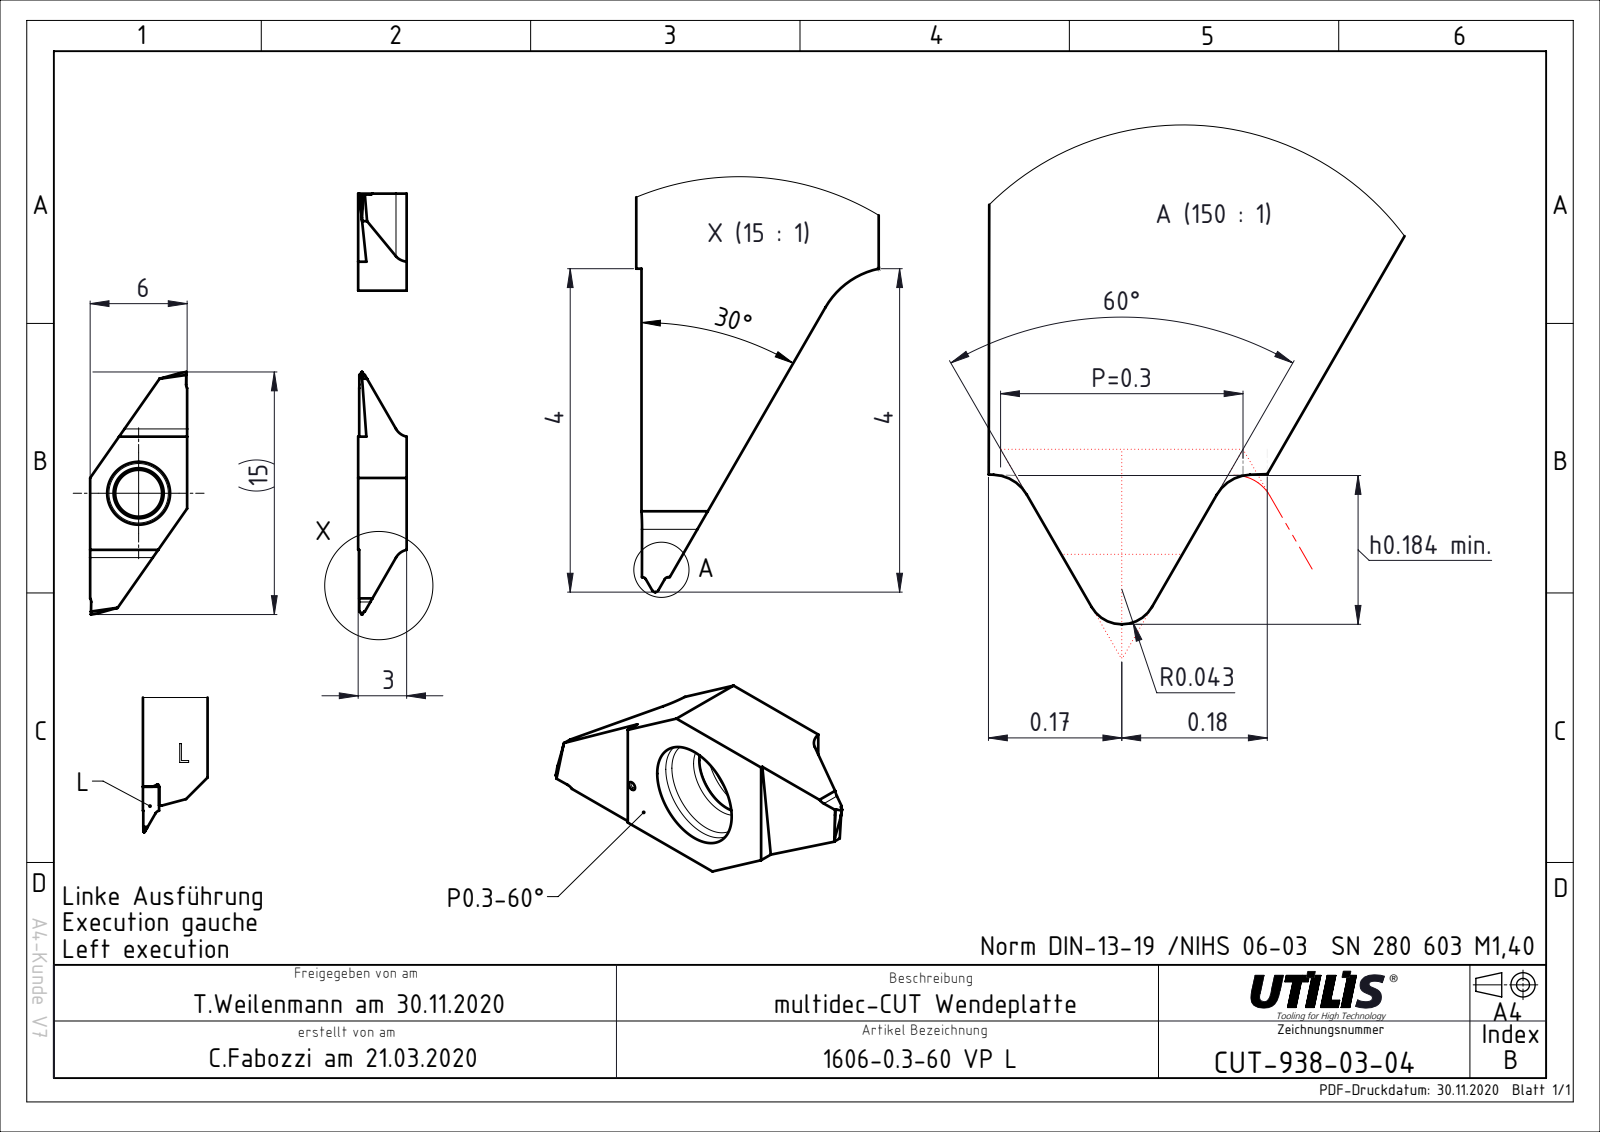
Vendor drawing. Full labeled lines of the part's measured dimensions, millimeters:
Part name (STEP PRODUCT): CUT-938-03; ASME Y14.5
STEP written by: FormatWorks Professional (AP242_MANAGED_MODEL_BASED_3D_ENGINEERING_MIM_LF)
Units: millimetres
Bodies: 1 solid, 40 faces (22 planar, 14 cylindrical, 4 other)
Overall size (bounding box): 15 × 6 × 3
Volume: 128 mm³ · Surface area: 211 mm²
Round holes (diameter × count): ⌀2.9 ×1
Partial cylindrical surfaces — rounded edges, fillets, slot ends (radius × count): R1 ×2
Main face-to-face distances: 6, 3, 9, 12, 11.15, 7, 13.15, 13.16
